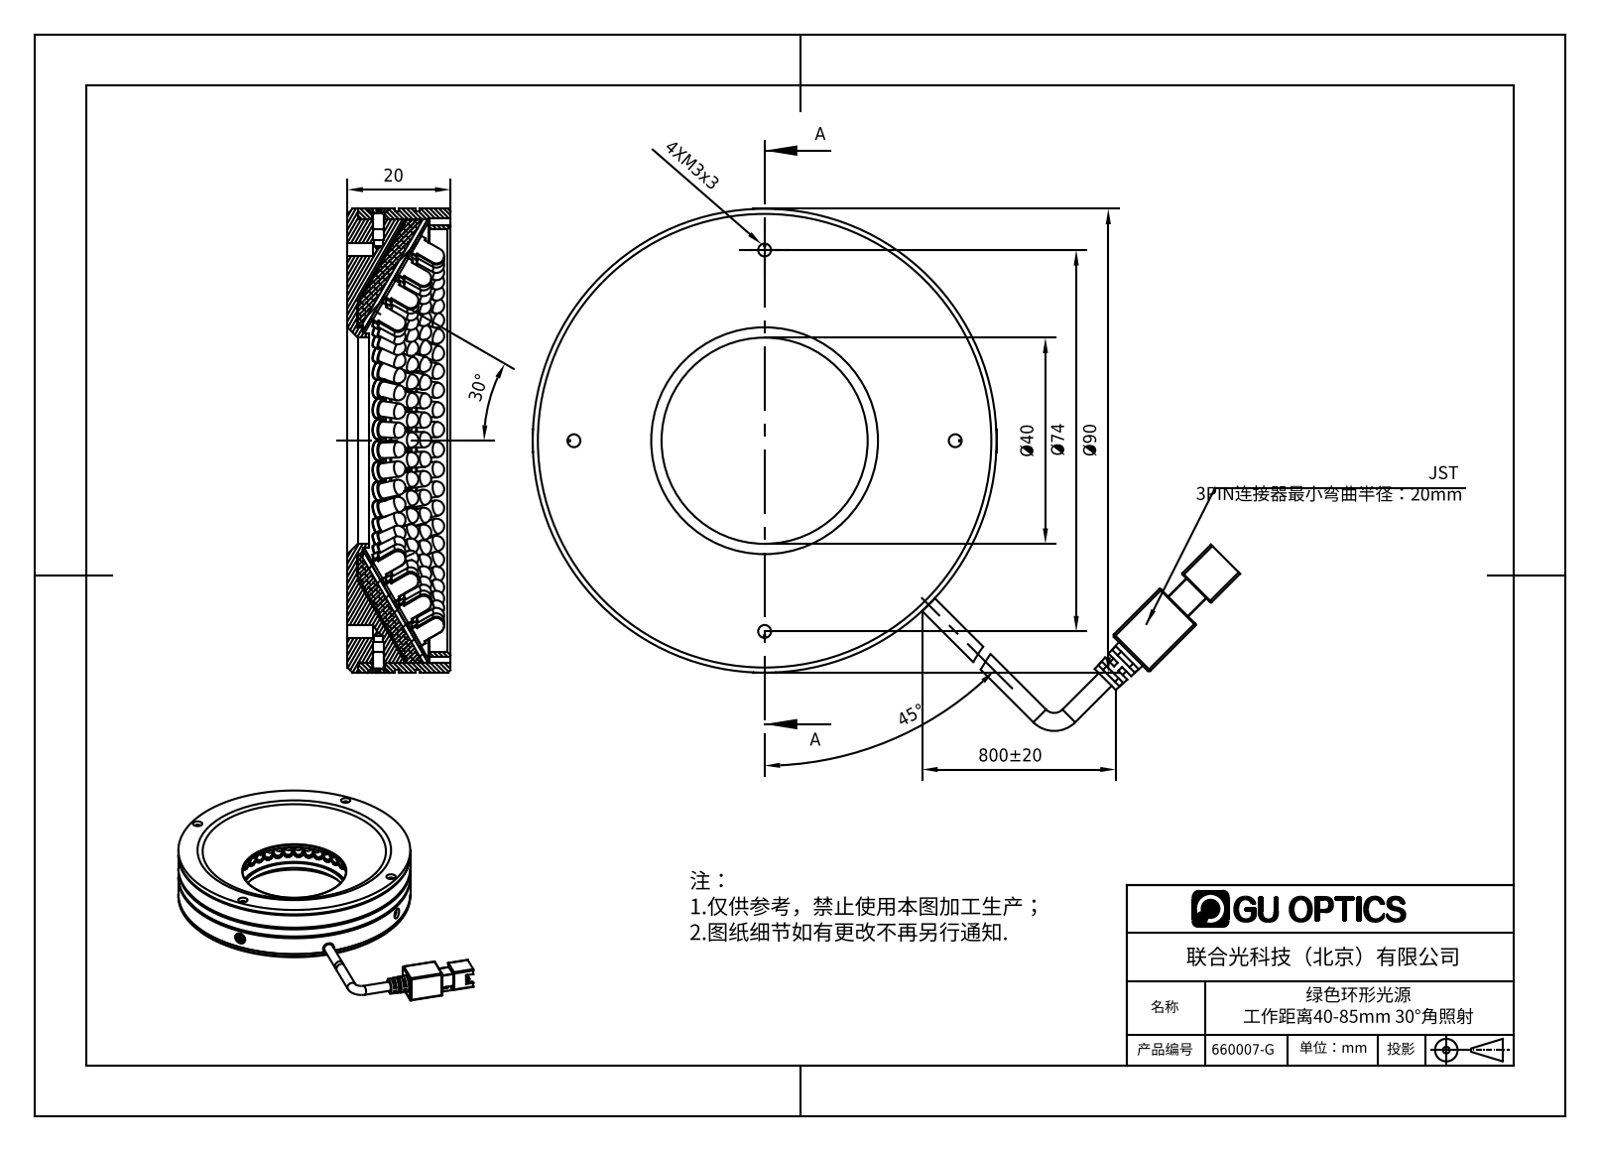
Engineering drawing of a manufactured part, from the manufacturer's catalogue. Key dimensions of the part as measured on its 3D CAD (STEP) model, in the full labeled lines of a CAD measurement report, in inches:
Part name (STEP PRODUCT): 660007-G
STEP written by: SolidWorks 2016 (AUTOMOTIVE_DESIGN)
Units: inches
Bodies: 201 solids, 4314 faces (2669 planar, 1337 cylindrical, 308 other)
Overall size (bounding box): 5.405 × 3.989 × 0.951
Volume: 4.808 in³ · Surface area: 122 in²
Round holes (diameter × count): ⌀0.049 ×4, ⌀0.071 ×4, ⌀0.098 ×4, ⌀0.063 ×2, ⌀0.079 ×2, ⌀0.094 ×2, ⌀1.575 ×1, ⌀1.732 ×1, ⌀3.228 ×1
Round bosses / shafts (diameter × count): ⌀0.15 ×248, ⌀0.118 ×192, ⌀0.138 ×2, ⌀3.543 ×1, ⌀3.504 ×1, ⌀3.386 ×1, ⌀1.756 ×1, ⌀1.642 ×1
Partial cylindrical surfaces — rounded edges, fillets, slot ends (radius × count): R0.008 ×37, R0.004 ×15, R0.016 ×12, R0.012 ×1, R0.027 ×1, R0.055 ×1, R0.065 ×1, R0.354 ×1
Main face-to-face distances: 0.787, 0.079, 0.866, 0.709, 0.039, 0.02, 0.157, 0.236, 0.118, 0.551
Hole centre spacings: 0.217, 1.673, 2.219, 3.13, 3.346, 2.366, 1.457, 2.06
